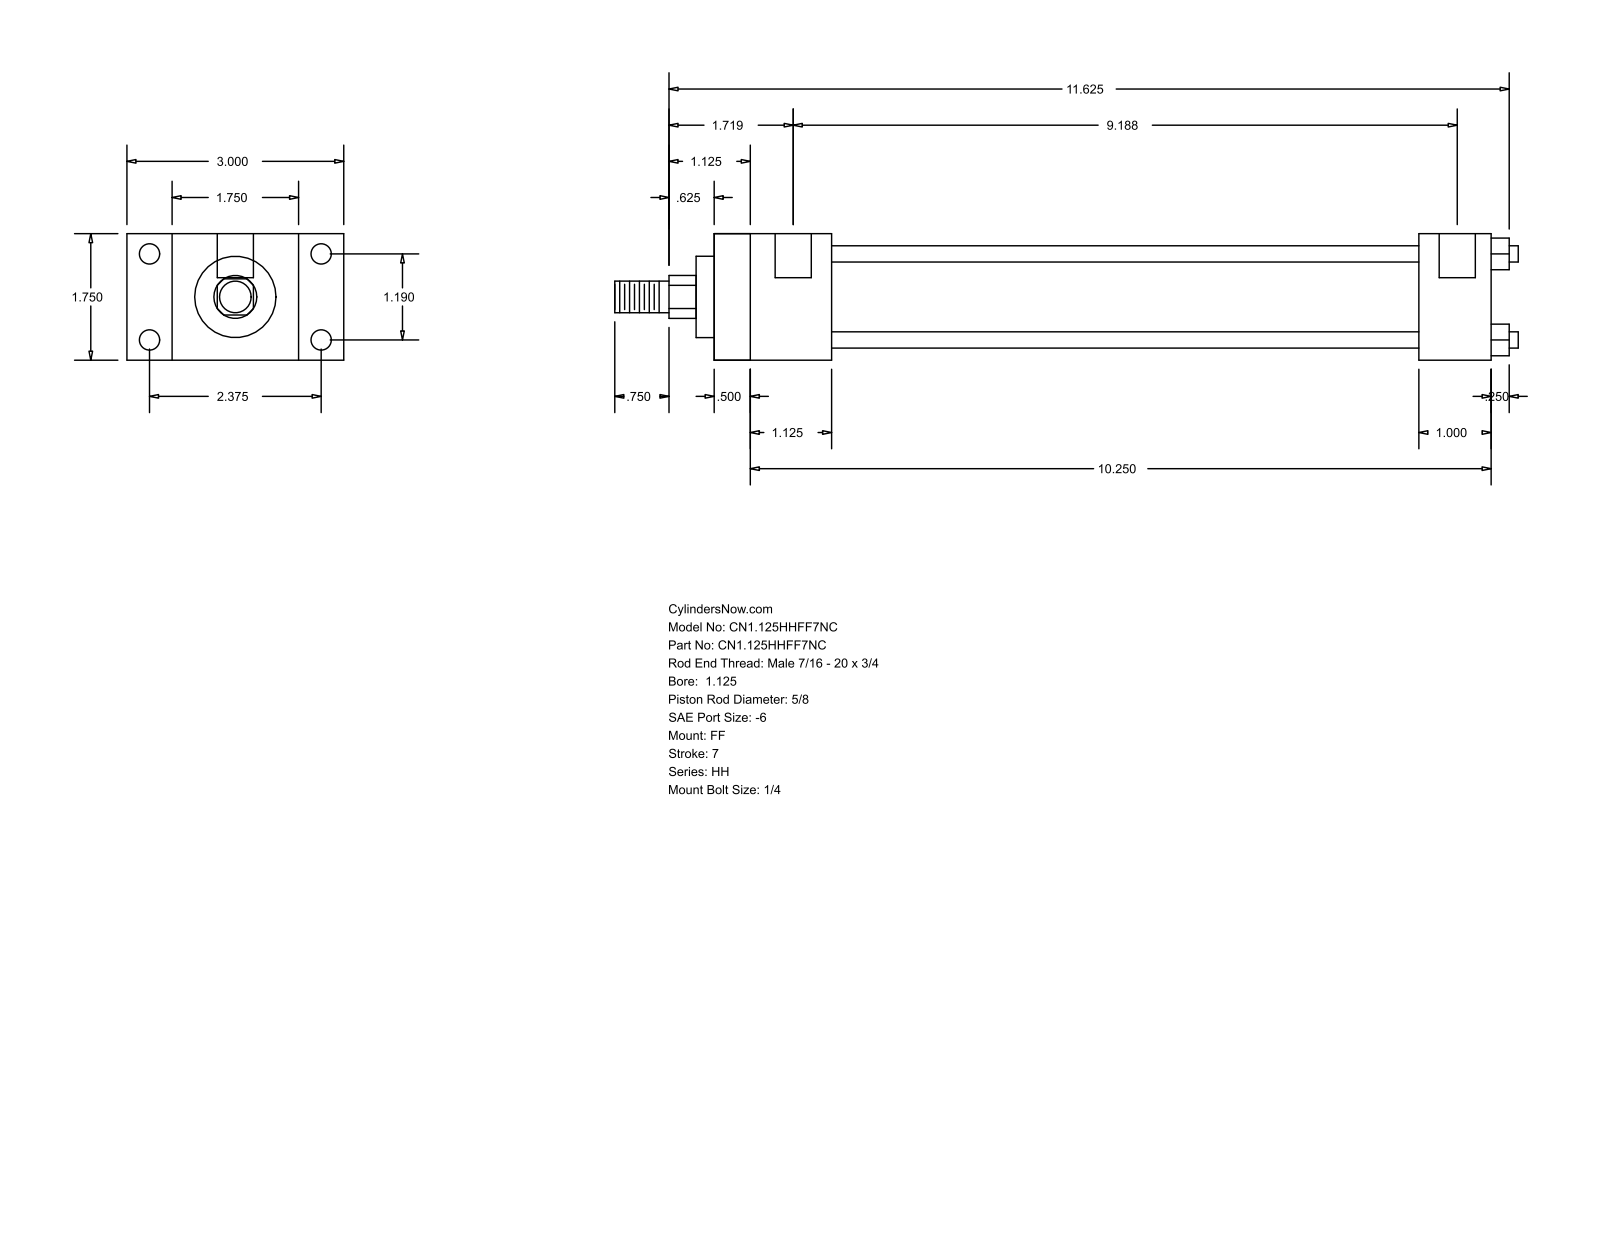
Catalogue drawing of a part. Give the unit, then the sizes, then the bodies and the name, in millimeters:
Units: millimetres
Overall size (bounding box): 317.5 × 76.2 × 44.45
Round holes (diameter × count): ⌀5.56 ×4, ⌀7.14 ×4, ⌀12.7 ×2
Round bosses / shafts (diameter × count): ⌀5.71 ×4, ⌀34.92 ×1, ⌀28.57 ×1, ⌀15.88 ×1, ⌀11.11 ×1
Partial cylindrical surfaces — rounded edges, fillets, slot ends (radius × count): R7.54 ×1
Main face-to-face distances: 44.46, 273.05, 15.87, 12.69, 260.36, 28.58, 60.33, 41.27, 247.64, 234.95
Hole centre spacings: 30.22, 60.32, 67.47, 230.19, 3.17, 233.36
Bodies: 0 solids, 92 faces (64 planar, 28 cylindrical, 0 other)
Part name (STEP PRODUCT): HH_FF__0112_0.625
STEP written by: GSSL Pune (CONFIG_CONTROL_DESIGN)
